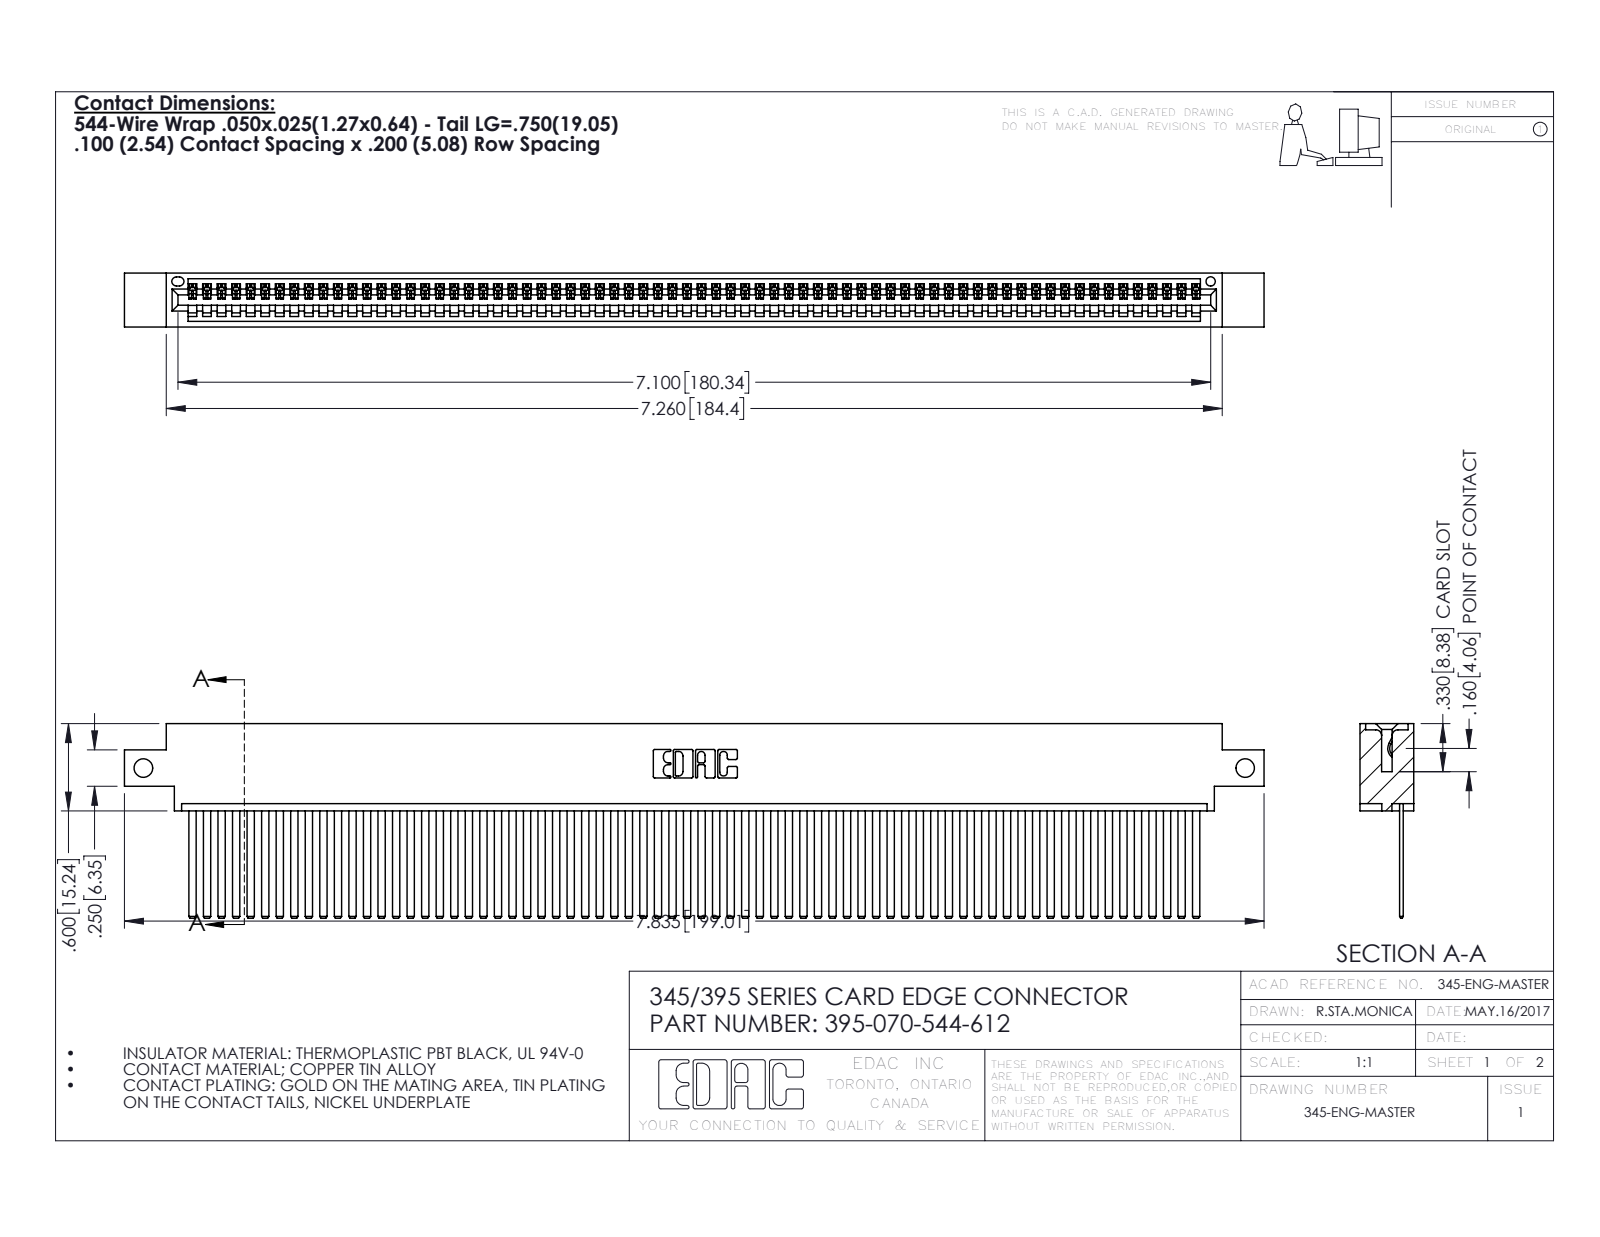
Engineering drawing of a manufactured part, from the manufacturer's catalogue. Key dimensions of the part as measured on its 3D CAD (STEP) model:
Part name (STEP PRODUCT): 345-292-001_345-293-144; 395-070-544-612; 345 Part_0.170 Offset - Side Mount
STEP written by: SolidWorks 2016 (CONFIG_CONTROL_DESIGN)
Units: inches
Bodies: 71 solids, 3770 faces (2604 planar, 1166 cylindrical, 0 other)
Overall size (bounding box): 7.835 × 1.337 × 0.37
Volume: 1.205 in³ · Surface area: 45 in²
Round holes (diameter × count): ⌀0.128 ×2, ⌀0.064 ×1
Partial cylindrical surfaces — rounded edges, fillets, slot ends (radius × count): R0.006 ×140, R0.01 ×22, R0.007 ×6, R0.031 ×6, R0.026 ×3, R0.031 ×2, R0.04 ×2, R0.014 ×1
Main face-to-face distances: 0.072, 0.298, 0.025, 0.098, 0.272, 0.37, 0.2, 0.225, 0.175, 0.149
Hole centre spacings: 7.575
